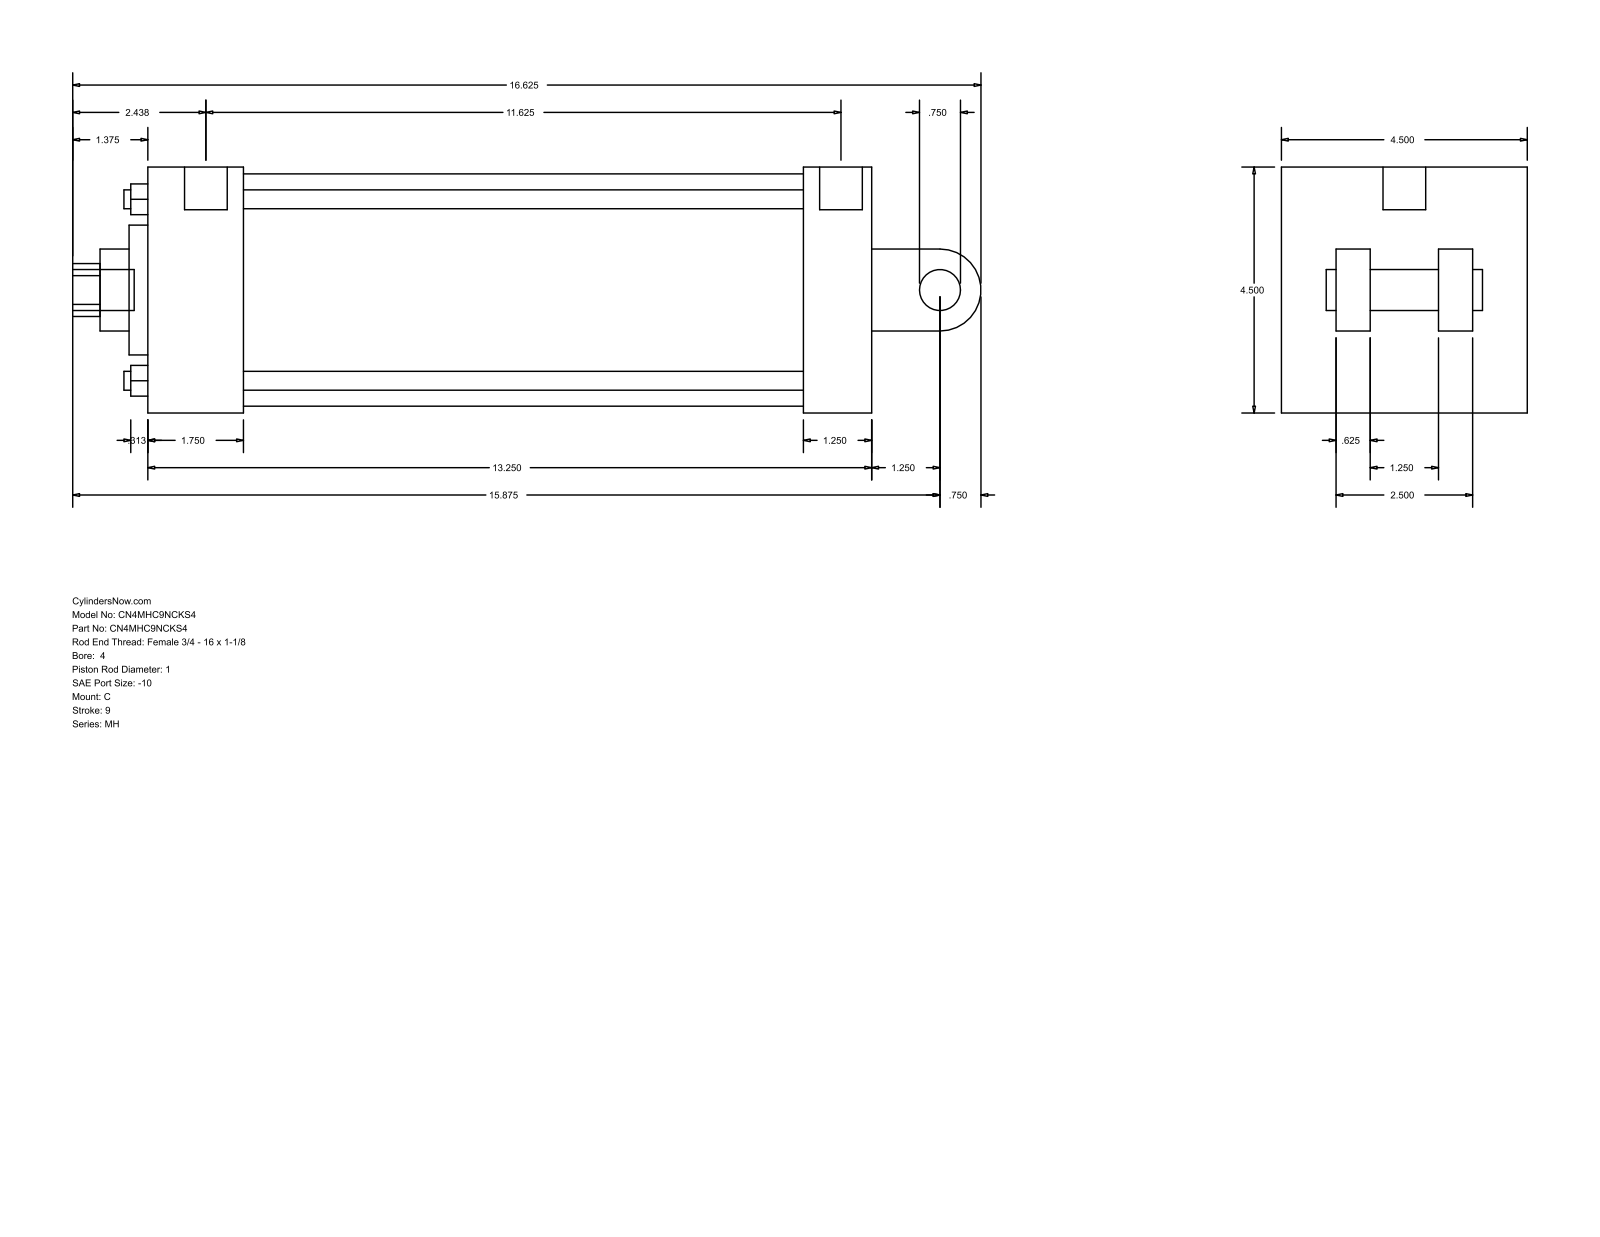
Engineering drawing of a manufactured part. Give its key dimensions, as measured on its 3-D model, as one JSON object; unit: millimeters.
{"part_name": "MH_C__0400_1", "step_written_by": "GSSL Pune (CONFIG_CONTROL_DESIGN)", "units": "millimeters", "bodies": {"solids": 0, "faces": 101, "planar": 71, "cylindrical": 30, "other": 0}, "overall_size": [422.27, 114.3, 114.3], "round_holes": [[8.76, 4], [8.73, 2], [19.84, 1], [25.4, 1], [38.1, 1], [60.33, 1], [107.95, 1]], "round_bosses_or_shafts": [[19.05, 2], [8.73, 2], [19.84, 1]], "partial_cylinders_radius": [[12.29, 1], [19.05, 1]], "face_to_face_distances": [114.3, 336.56, 44.46, 304.81, 260.35, 292.1, 31.75, 73.03, 15.87, 47.63], "hole_center_spacings": [59.62, 84.32, 119.25, 1.58]}
